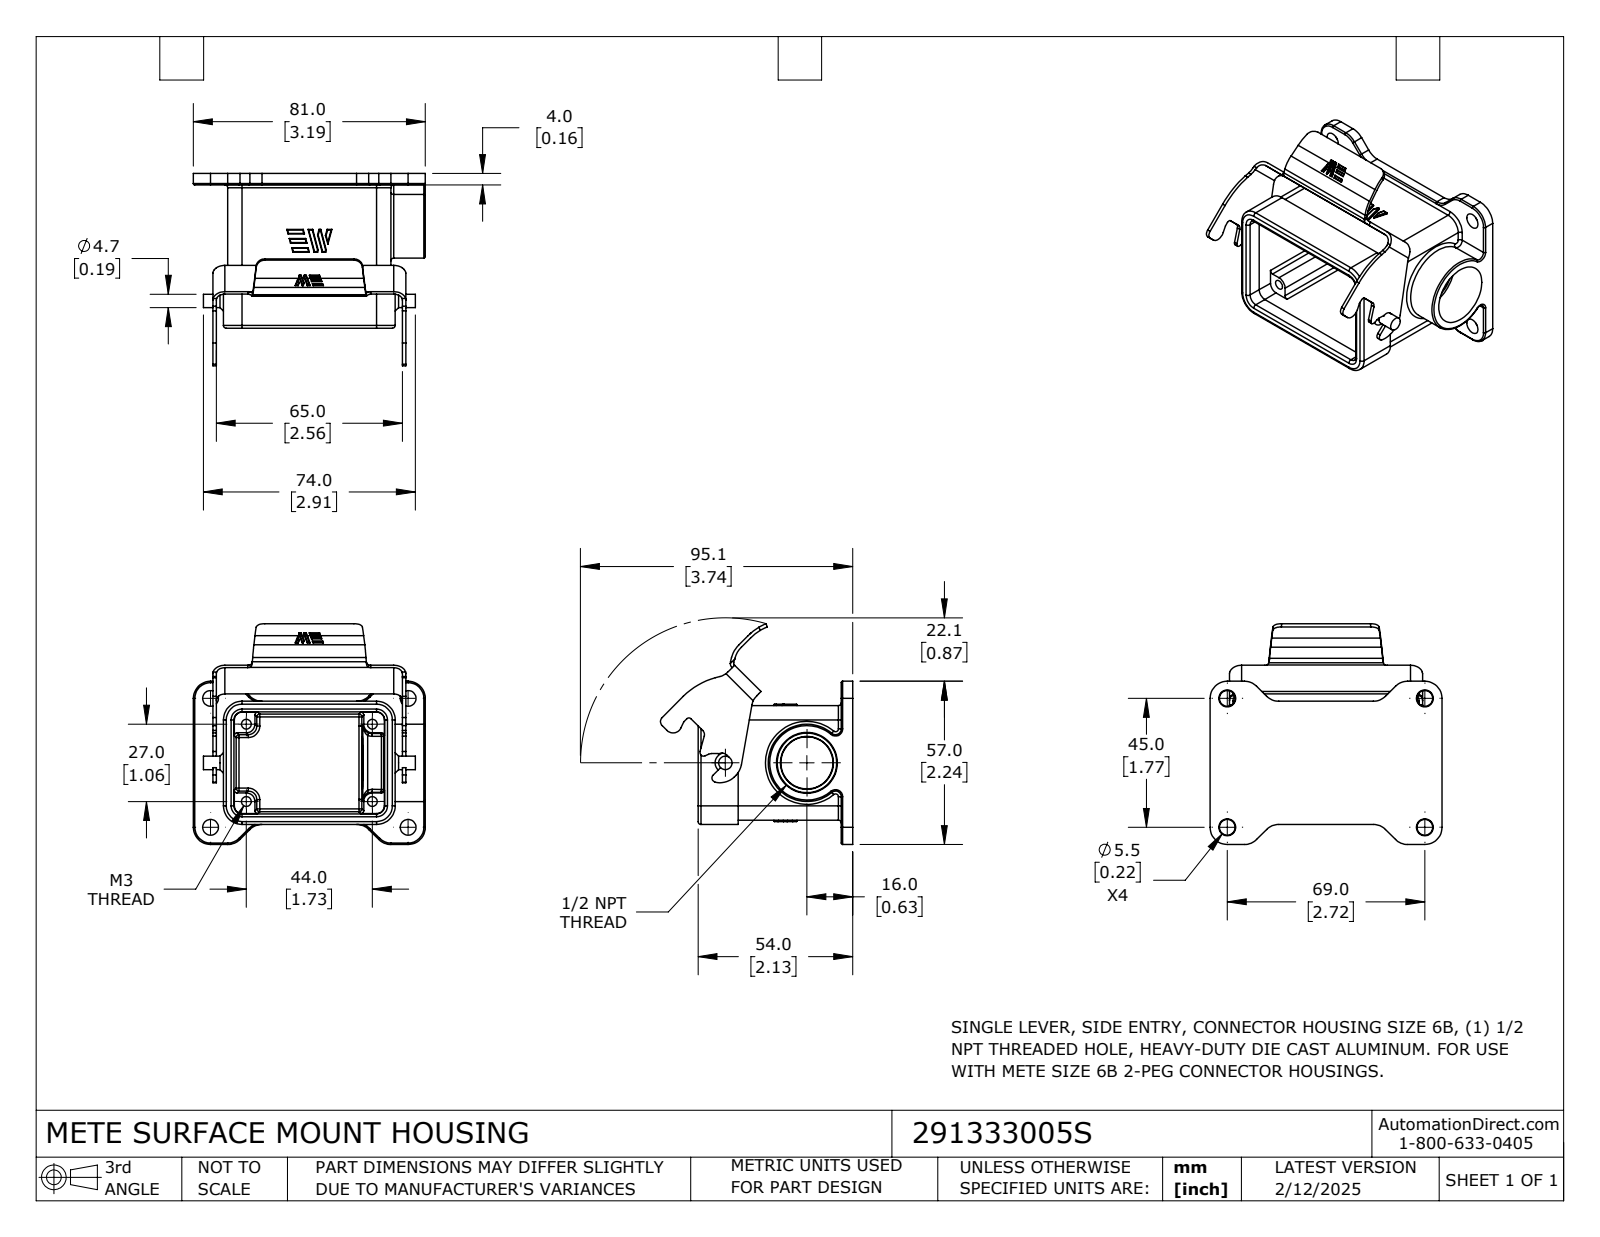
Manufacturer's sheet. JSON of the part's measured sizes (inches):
{"part_name": "291333005S", "step_written_by": "SolidWorks 2024 (CONFIG_CONTROL_DESIGN)", "units": "inches", "bodies": {"solids": 1, "faces": 465, "planar": 174, "cylindrical": 220, "other": 71}, "overall_size": [3.189, 3.034, 2.644], "volume_in3": 3.439, "surface_area_in2": 54.34, "round_holes": [[0.134, 4]], "round_bosses_or_shafts": [[0.185, 1]], "partial_cylinders_radius": [[0.008, 50], [0.039, 33], [0.236, 14], [0.02, 10], [0.118, 9], [0.079, 6], [0.11, 4], [0.197, 4]], "face_to_face_distances": [0.157, 0.059, 0.047, 1.575, 1.634, 0.146, 2.606, 0.205, 2.402, 2.449], "hole_center_spacings": [1.063, 1.732, 2.032]}
